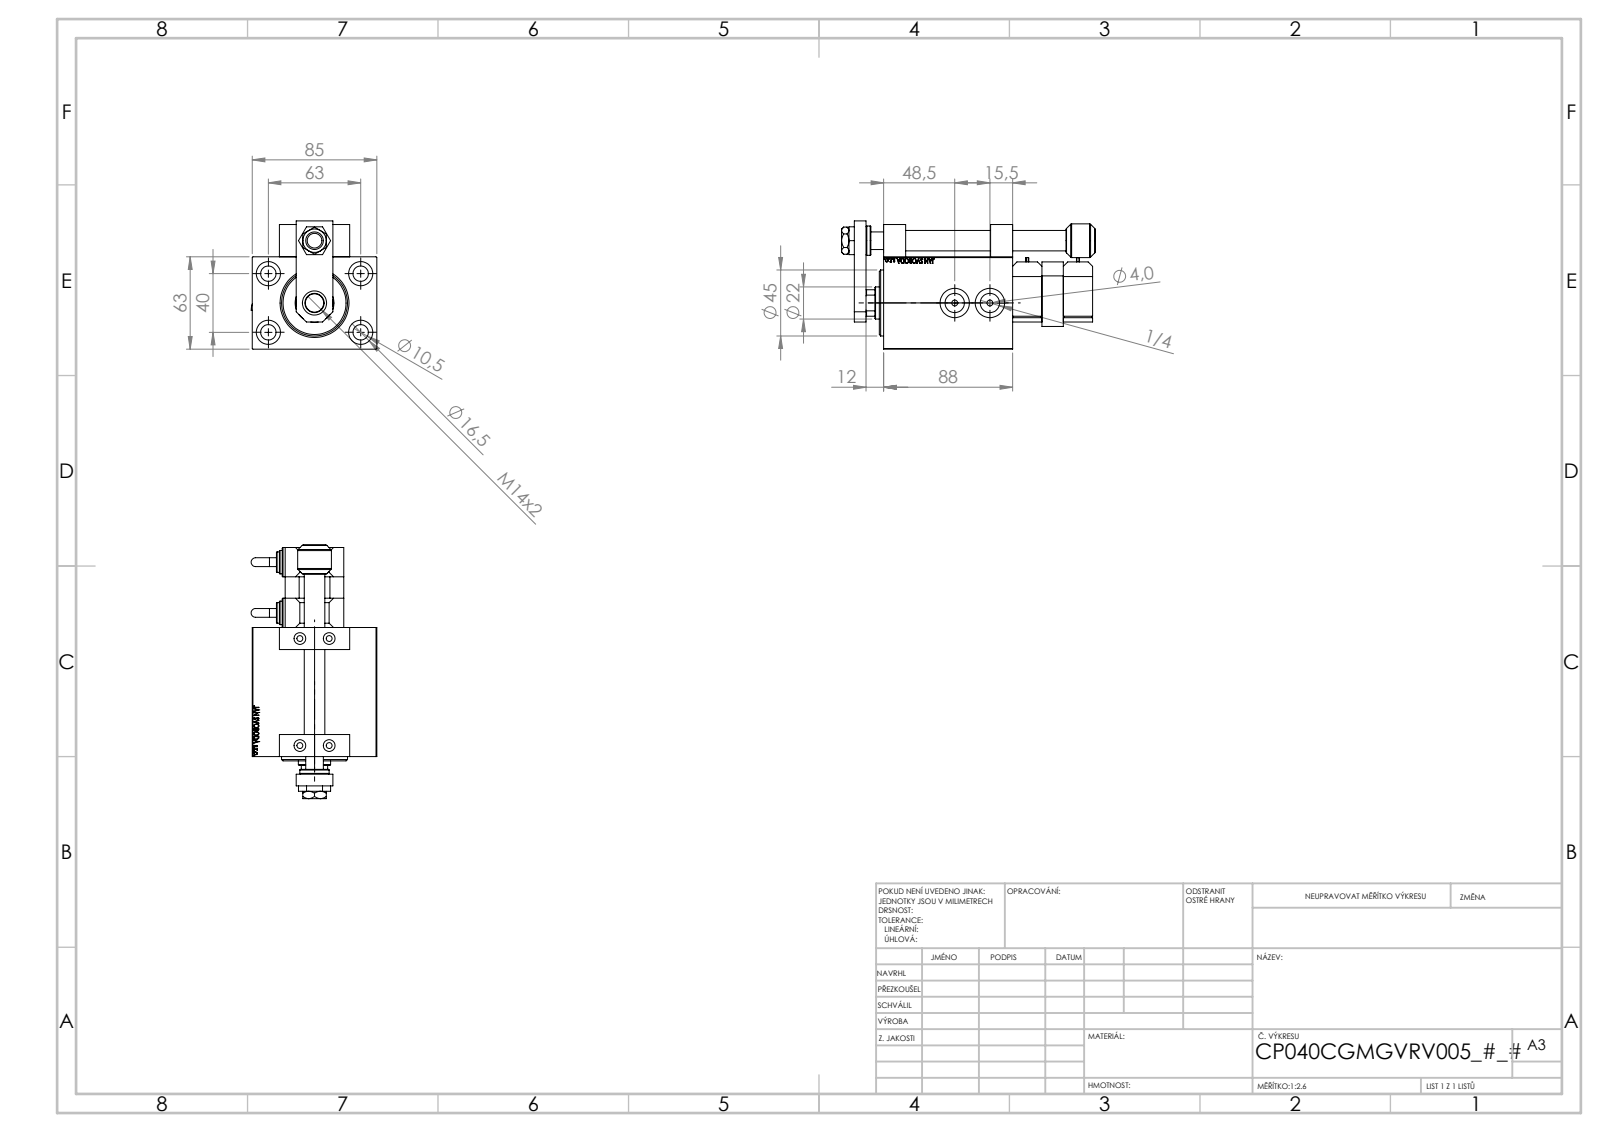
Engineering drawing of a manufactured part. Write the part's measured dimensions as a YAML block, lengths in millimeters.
part_name: "NUT_D19_P; V450CP_VC_B; SWITCH P; KROUZEK_PRO_TYC (+7 more)"
step_written_by: "SolidWorks 2019 (CONFIG_CONTROL_DESIGN)"
units: millimeters
bodies: {solids: 14, faces: 1110, planar: 525, cylindrical: 132, other: 453}
overall_size: [173.1, 87.5, 85.76]
volume: 581429
surface_area: 129953
round_holes:
  - {diameter: 4, count: 8}
  - {diameter: 16.5, count: 5}
  - {diameter: 8, count: 4}
  - {diameter: 10.5, count: 4}
  - {diameter: 9.73, count: 2}
  - {diameter: 13.16, count: 2}
  - {diameter: 14, count: 2}
  - {diameter: 15, count: 2}
  - {diameter: 20, count: 2}
  - {diameter: 12, count: 1}
  - {diameter: 12.5, count: 1}
  - {diameter: 13, count: 1}
round_bosses_or_shafts:
  - {diameter: 20, count: 3}
  - {diameter: 16, count: 2}
  - {diameter: 14, count: 2}
  - {diameter: 6, count: 2}
  - {diameter: 23, count: 1}
partial_cylinders:
  - {radius: 3, count: 1}
  - {radius: 10.5, count: 1}
face_to_face_distances: [63, 85, 20, 88, 108, 34.6, 12, 32, 35, 76]
hole_center_spacings: [37.31, 20, 38.71, 39.3, 40, 63, 69.99, 70.88]
